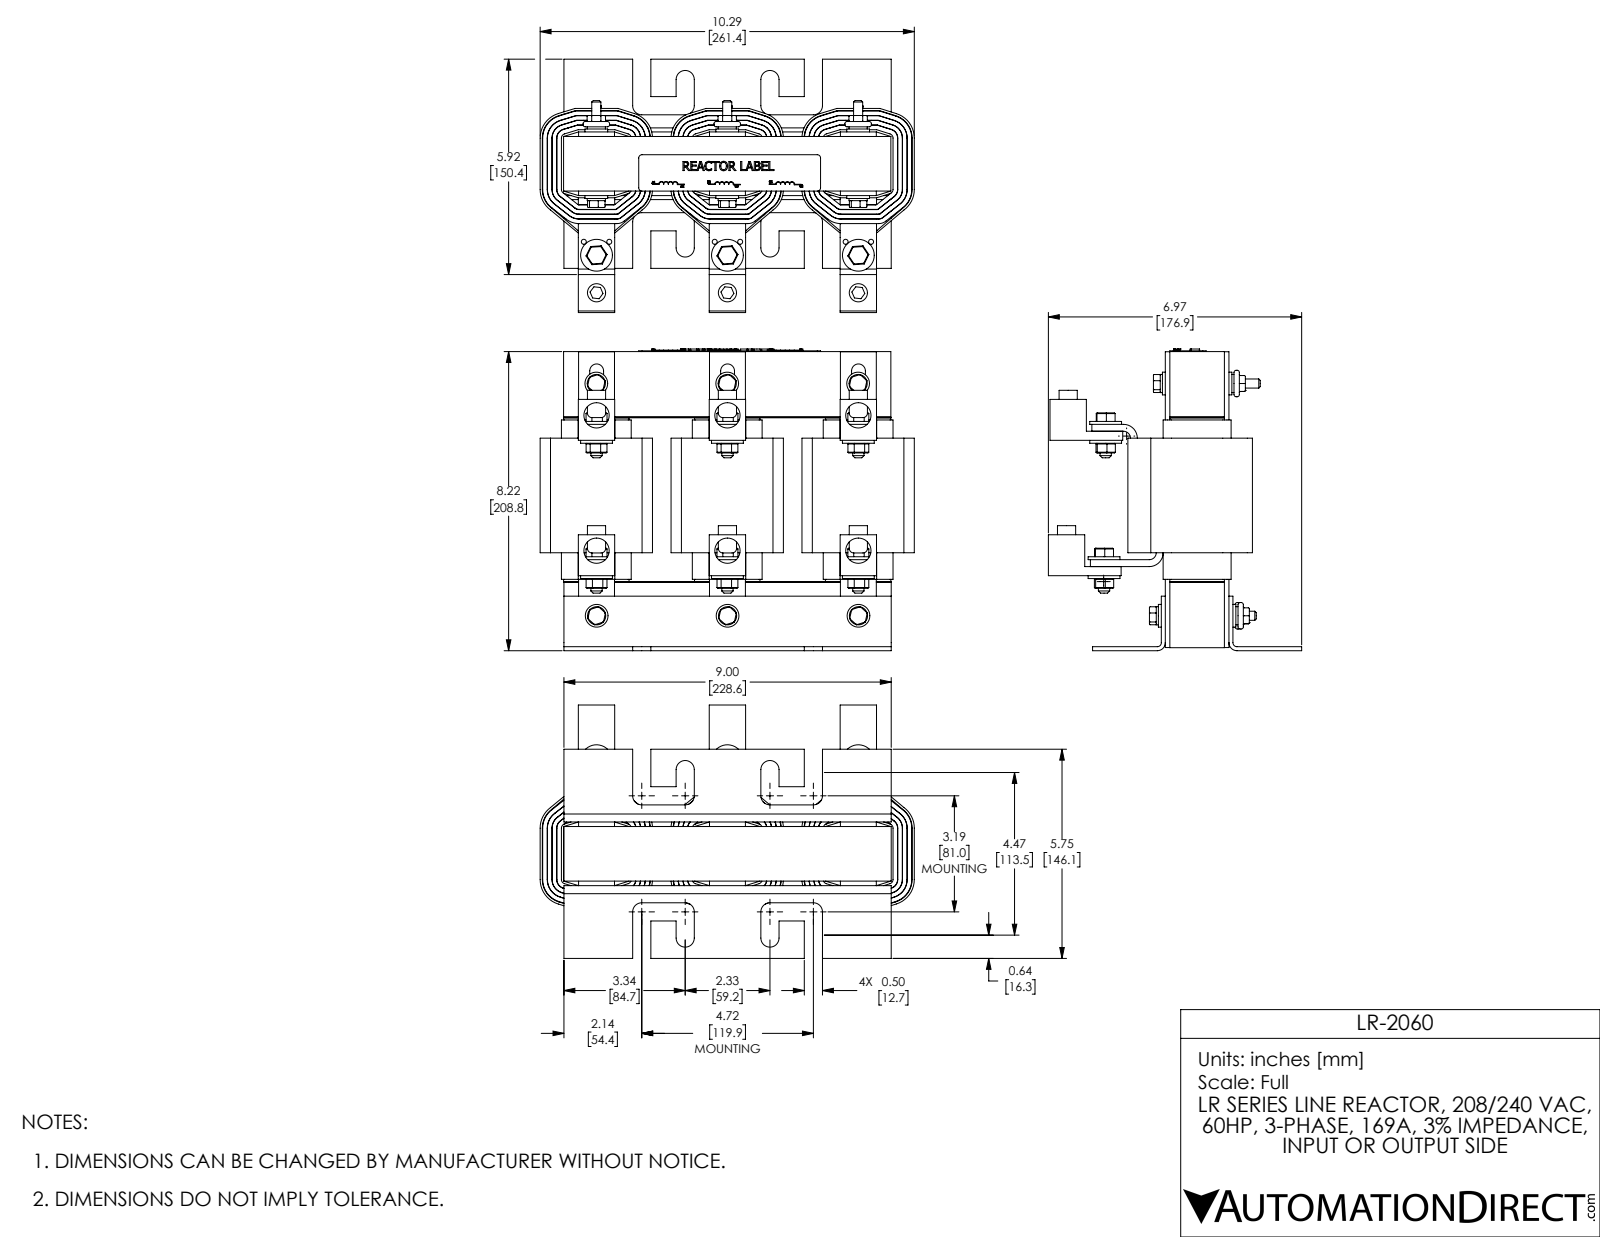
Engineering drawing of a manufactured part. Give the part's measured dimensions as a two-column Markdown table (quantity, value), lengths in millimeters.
| quantity | value |
| --- | --- |
| part name | LR-2060 |
| STEP written by | SolidWorks 2017 (AUTOMOTIVE_DESIGN) |
| units | millimeters |
| bodies | 91 solids, 2288 faces (1301 planar, 773 cylindrical, 214 other) |
| overall size | 261.4 × 210.6 × 176.9 |
| volume | 2 683 000 mm³ |
| surface area | 976 100 mm² |
| round holes (diameter × count) | 3.5 × 12, 6.1 × 6, 6.4 × 6, 7.1 × 6, 7.1 × 6, 7.9 × 6, 8.3 × 6, 8.6 × 6, 8.7 × 6, 17.7 × 6, 5 × 3, 9.7 × 3 |
| round bosses / shafts (diameter × count) | 12.7 × 12, 22.2 × 6, 18.5 × 6, 7.6 × 6, 15.9 × 5, 7 × 3, 15.9 × 1 |
| partial cylindrical surfaces (radius × count) | 0.5 × 72, 0.8 × 72, 6.4 × 24, 4.8 × 21, 1.5 × 15, 9.7 × 15, 2 × 12, 3 × 12 |
| main face-to-face distances | 3.3, 3.4, 3.2, 3.2, 6.5, 91.4, 38.1, 2.8, 6.6, 6.6 |
| hole center spacings | 91.4, 182.9, 91.4, 109.2, 1, 12.2, 12.9, 13 |
